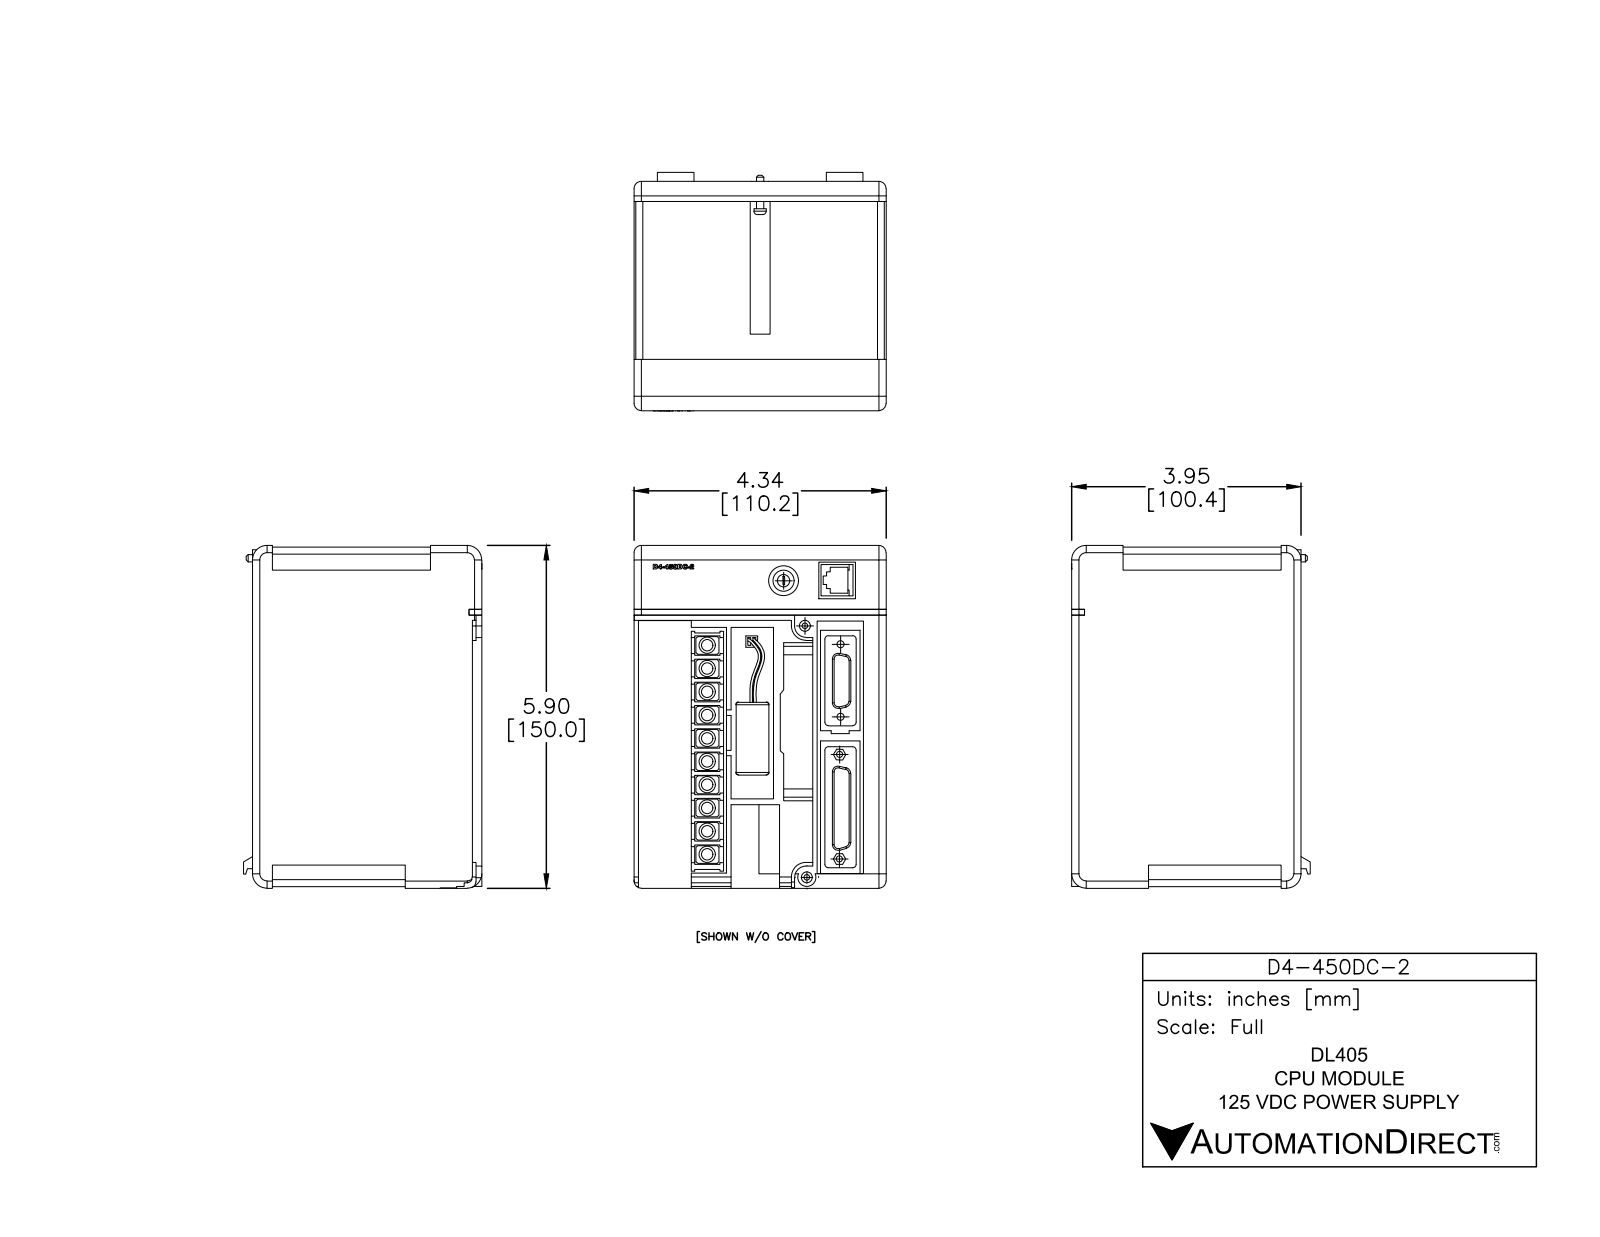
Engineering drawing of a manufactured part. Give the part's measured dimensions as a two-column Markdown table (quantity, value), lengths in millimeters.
| quantity | value |
| --- | --- |
| part name | D4-450DC-2 |
| STEP written by | SolidWorks 2014 (AUTOMOTIVE_DESIGN) |
| units | millimeters |
| bodies | 3 solids, 798 faces (595 planar, 110 cylindrical, 93 other) |
| overall size | 150 × 110.2 × 104.3 |
| volume | 1 470 000 mm³ |
| surface area | 116 400 mm² |
| round holes (diameter × count) | 2.5 × 2, 3 × 2, 2.6 × 1, 2.7 × 1, 4.8 × 1, 4.8 × 1, 5.5 × 1, 13 × 1 |
| round bosses / shafts (diameter × count) | 7.1 × 10, 14.4 × 1, 9.3 × 1, 5.4 × 1, 3.1 × 1 |
| partial cylindrical surfaces (radius × count) | 2.5 × 9, 1.5 × 8, 3.2 × 8, 0.8 × 6, 6.4 × 6, 3 × 4, 5.1 × 2, 3.7 × 1 |
| main face-to-face distances | 110.2, 0.8, 148.5, 149.2, 100.3, 18.2, 82.2, 11.4, 2.9, 2 |
| hole center spacings | 16.4, 16.5, 17.5, 21.9, 31.7, 37.3, 42.7, 45.7 |
